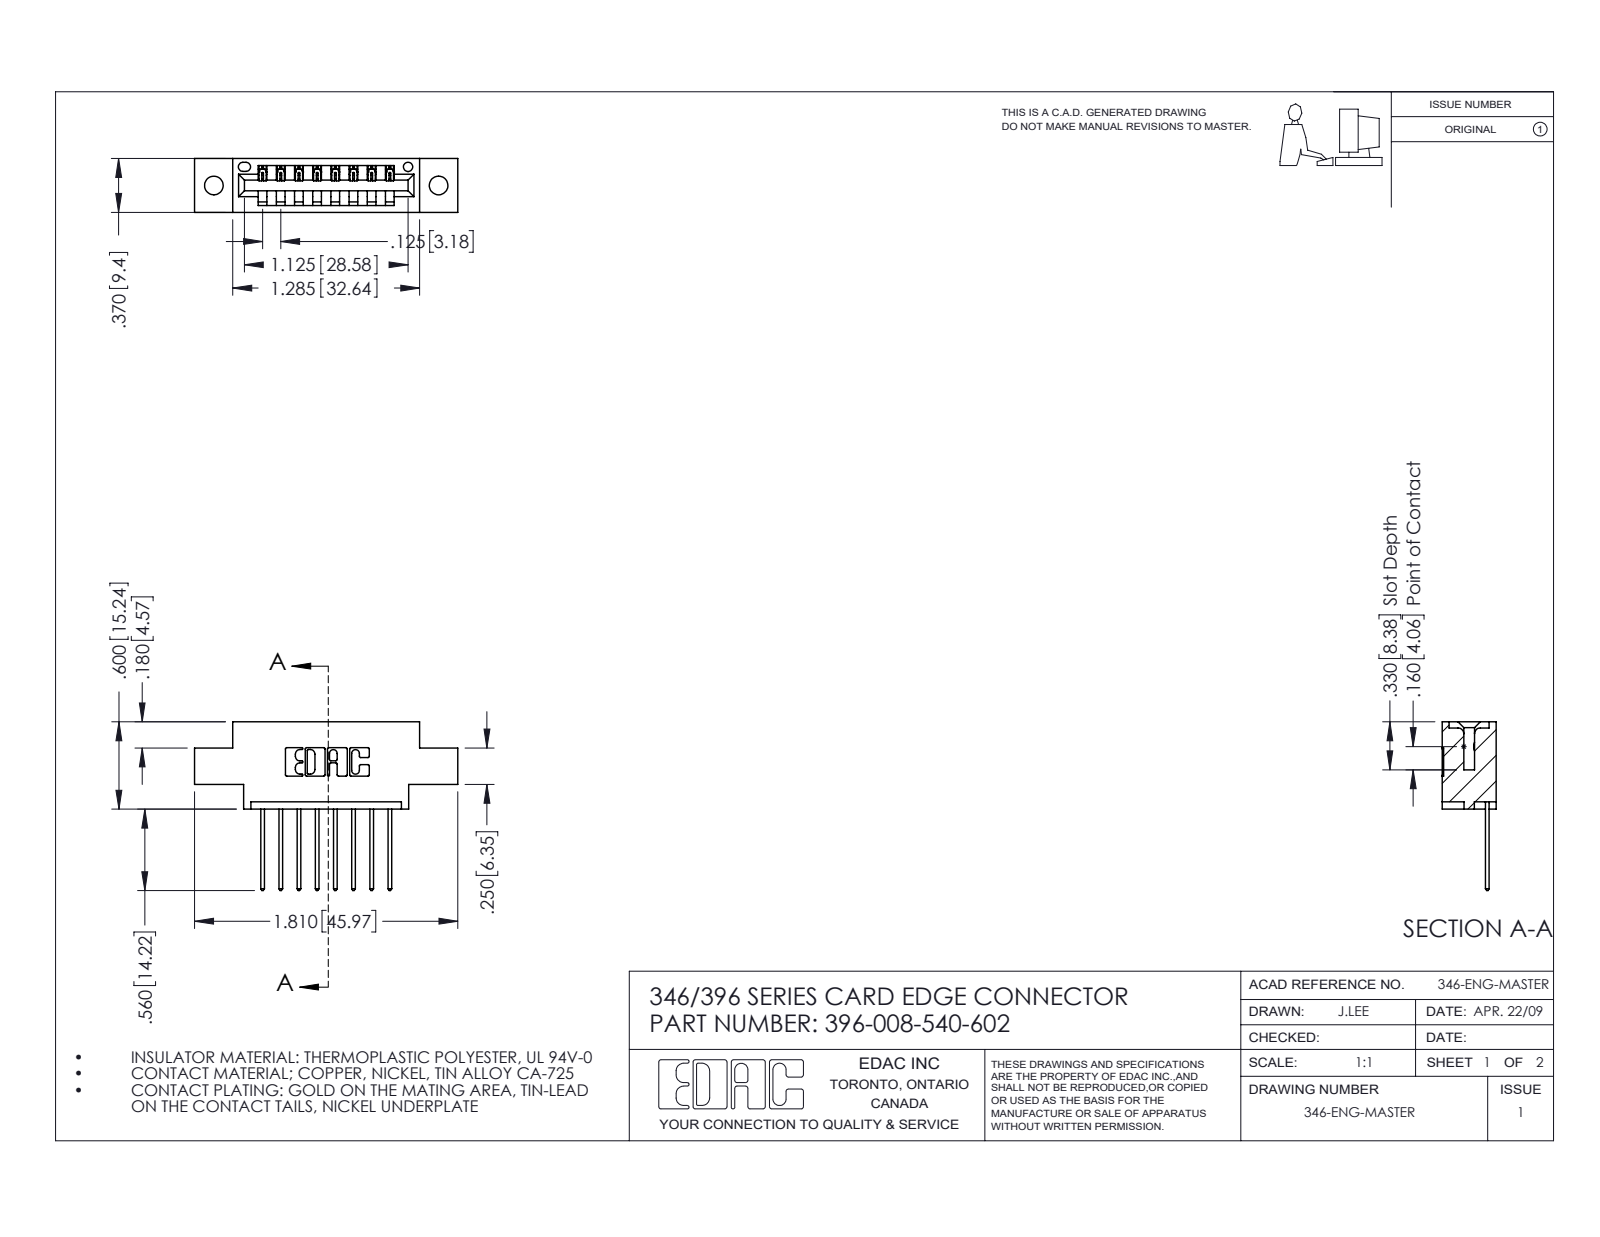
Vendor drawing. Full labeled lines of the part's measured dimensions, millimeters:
Part name (STEP PRODUCT): 396-008-540-602; 345-292-001_345-293-140; 346 Part_0.170 Offset - 0.128 Dia
STEP written by: SolidWorks 2016 (CONFIG_CONTROL_DESIGN)
Units: millimetres
Bodies: 9 solids, 590 faces (400 planar, 190 cylindrical, 0 other)
Overall size (bounding box): 46 × 29.5 × 9.4
Volume: 3 980 mm³ · Surface area: 4 583 mm²
Round holes (diameter × count): ⌀3.3 ×2, ⌀1.6 ×1
Partial cylindrical surfaces — rounded edges, fillets, slot ends (radius × count): R0.3 ×22, R0.2 ×16, R0.3 ×16, R0.2 ×6, R0.8 ×6, R0.7 ×3, R0.8 ×2, R1 ×2
Main face-to-face distances: 6.4, 9.4, 1.2, 8.2, 1.8, 7.6, 0.6, 3.8, 5.6, 2.5
Hole centre spacings: 6.2, 34.1, 39.2
